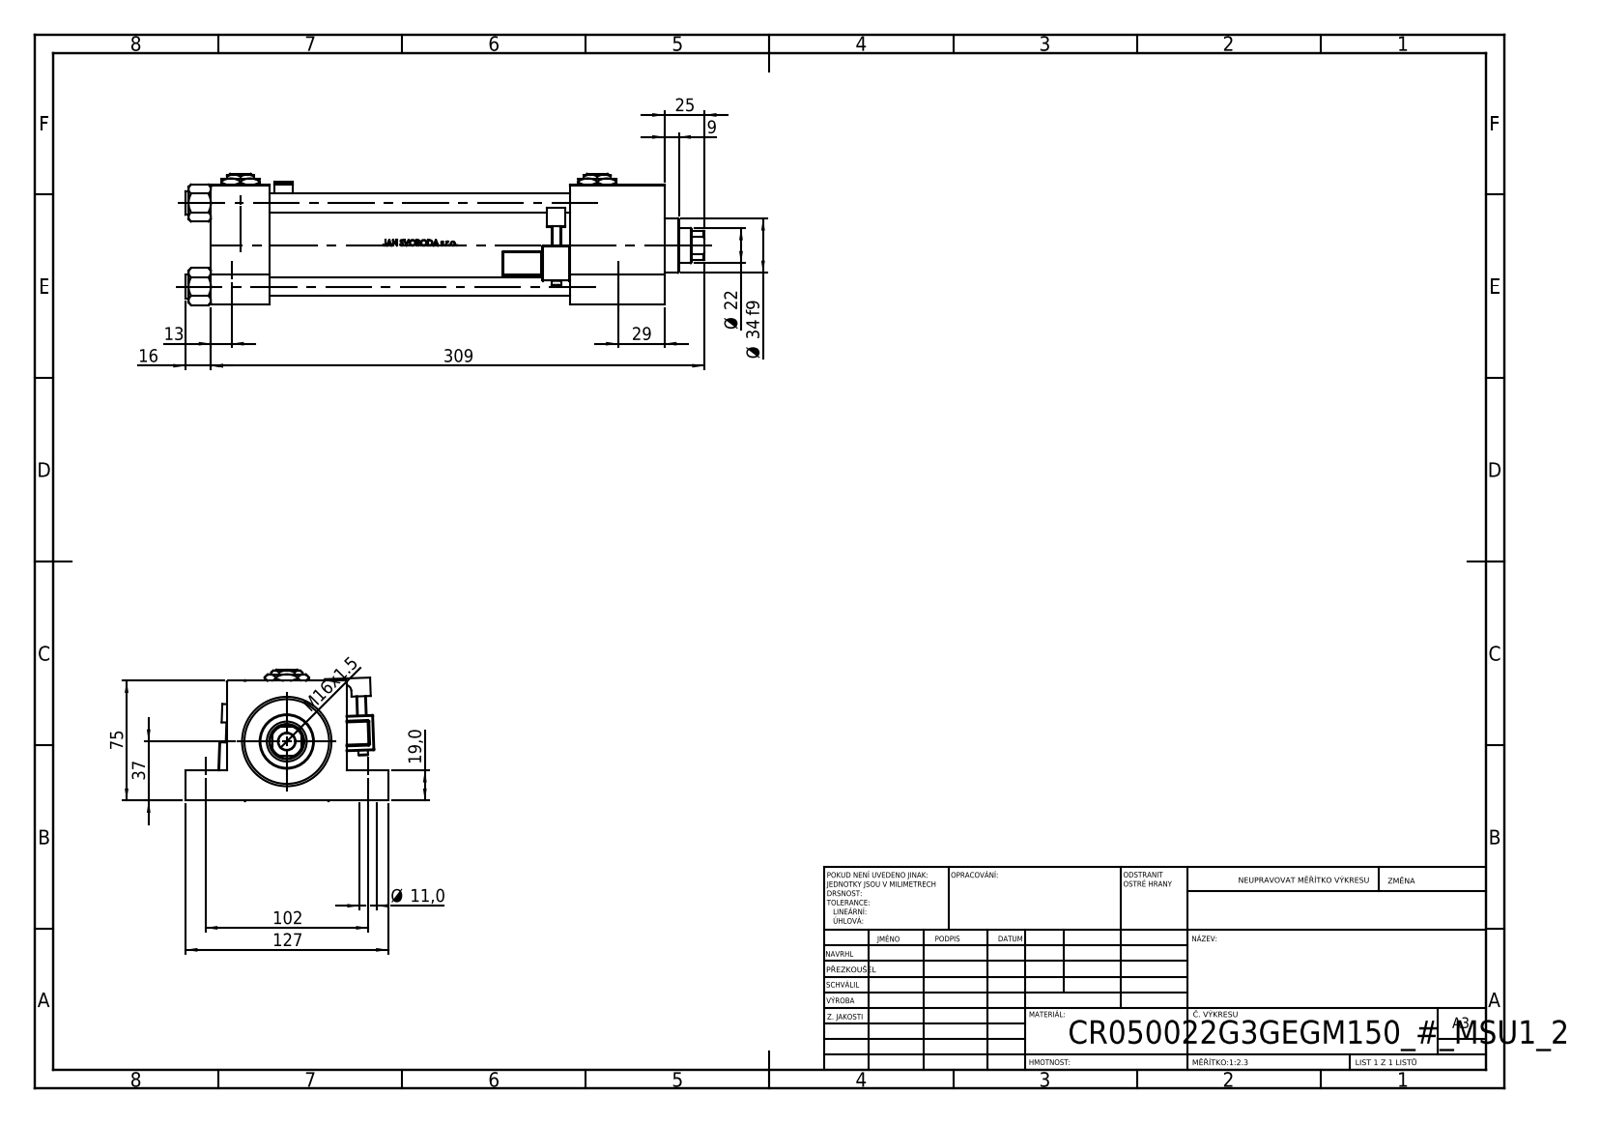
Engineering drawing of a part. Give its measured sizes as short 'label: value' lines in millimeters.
name: V215CR_G_Body; V215CR_G_TYCINKA; V215_VC_A; Zatka_pro_OIL_PORT (+3 more)
written by: SolidWorks 2019 (CONFIG_CONTROL_DESIGN)
unit: mm
bodies: 15 solids, 1326 faces (534 planar, 184 cylindrical, 608 other)
size: 325 × 127 × 82.27
volume: 975 535 mm³; area: 246 441 mm²
holes: 4× ⌀11, 4× ⌀12, 2× ⌀7, 2× ⌀20.96, 2× ⌀30, 1× ⌀10.5, 1× ⌀22, 1× ⌀25, 1× ⌀41, 1× ⌀50, 1× ⌀53
bosses: 4× ⌀15, 2× ⌀6, 1× ⌀56, 1× ⌀34
rounds: 48× R0.5, 2× R1, 2× R2.5, 2× R4, 1× R6, 1× R10.5
face distances: 75, 37, 284, 247, 225, 188, 59, 56, 19, 26
hole spacings: 52.3, 36.63, 37.34, 51.3, 52.63, 73.96, 102, 234.61
